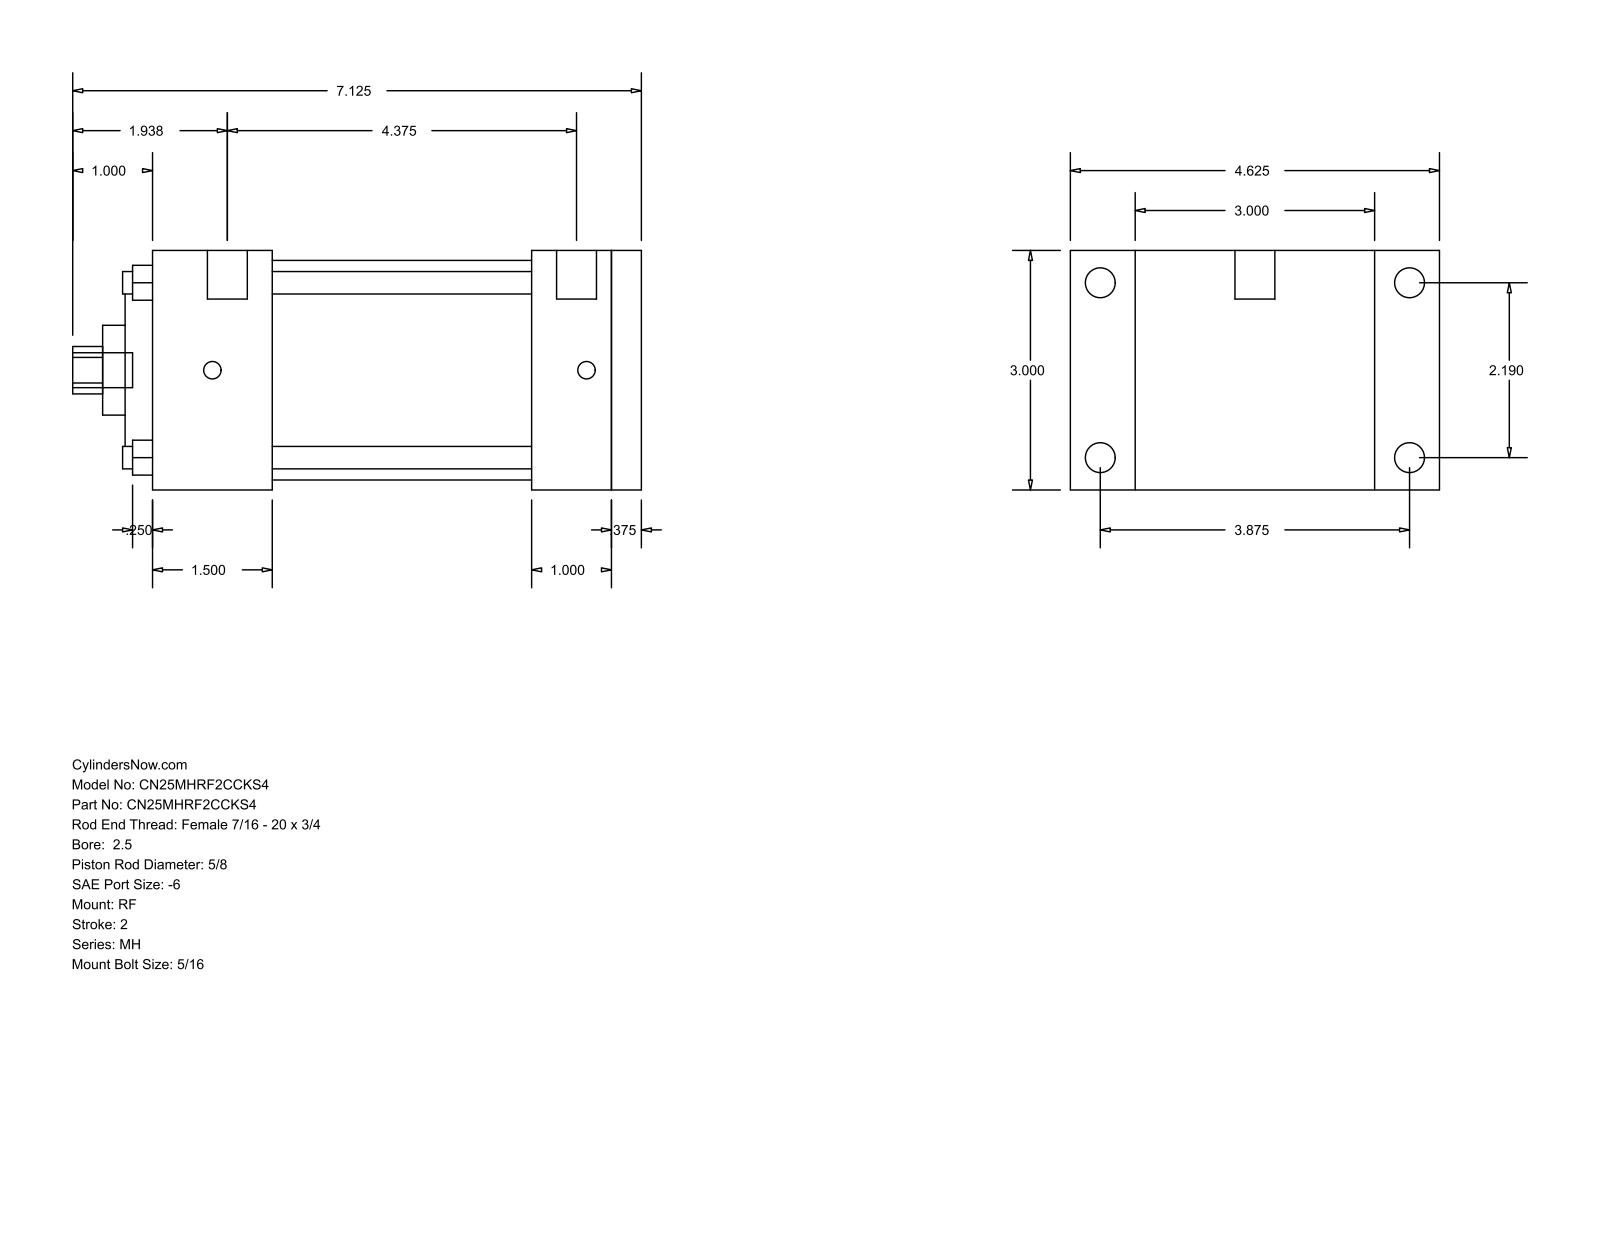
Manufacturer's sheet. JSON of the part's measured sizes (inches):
{"part_name": "MH_RF__0250_0.625", "step_written_by": "GSSL Pune (CONFIG_CONTROL_DESIGN)", "units": "inches", "bodies": {"solids": 0, "faces": 94, "planar": 65, "cylindrical": 29, "other": 0}, "overall_size": [7.125, 4.625, 3], "round_holes": [[0.281, 4], [0.625, 1], [1.125, 1], [2.187, 1], [2.75, 1]], "round_bosses_or_shafts": [[0.375, 4], [0.219, 4], [0.5, 2], [0.437, 1]], "partial_cylinders_radius": [[0.297, 1]], "face_to_face_distances": [3, 0.375, 6.125, 5.75, 1, 4.75, 1.375, 1.5, 3.25, 4.25], "hole_center_spacings": [1.548, 2.19, 3.097]}
